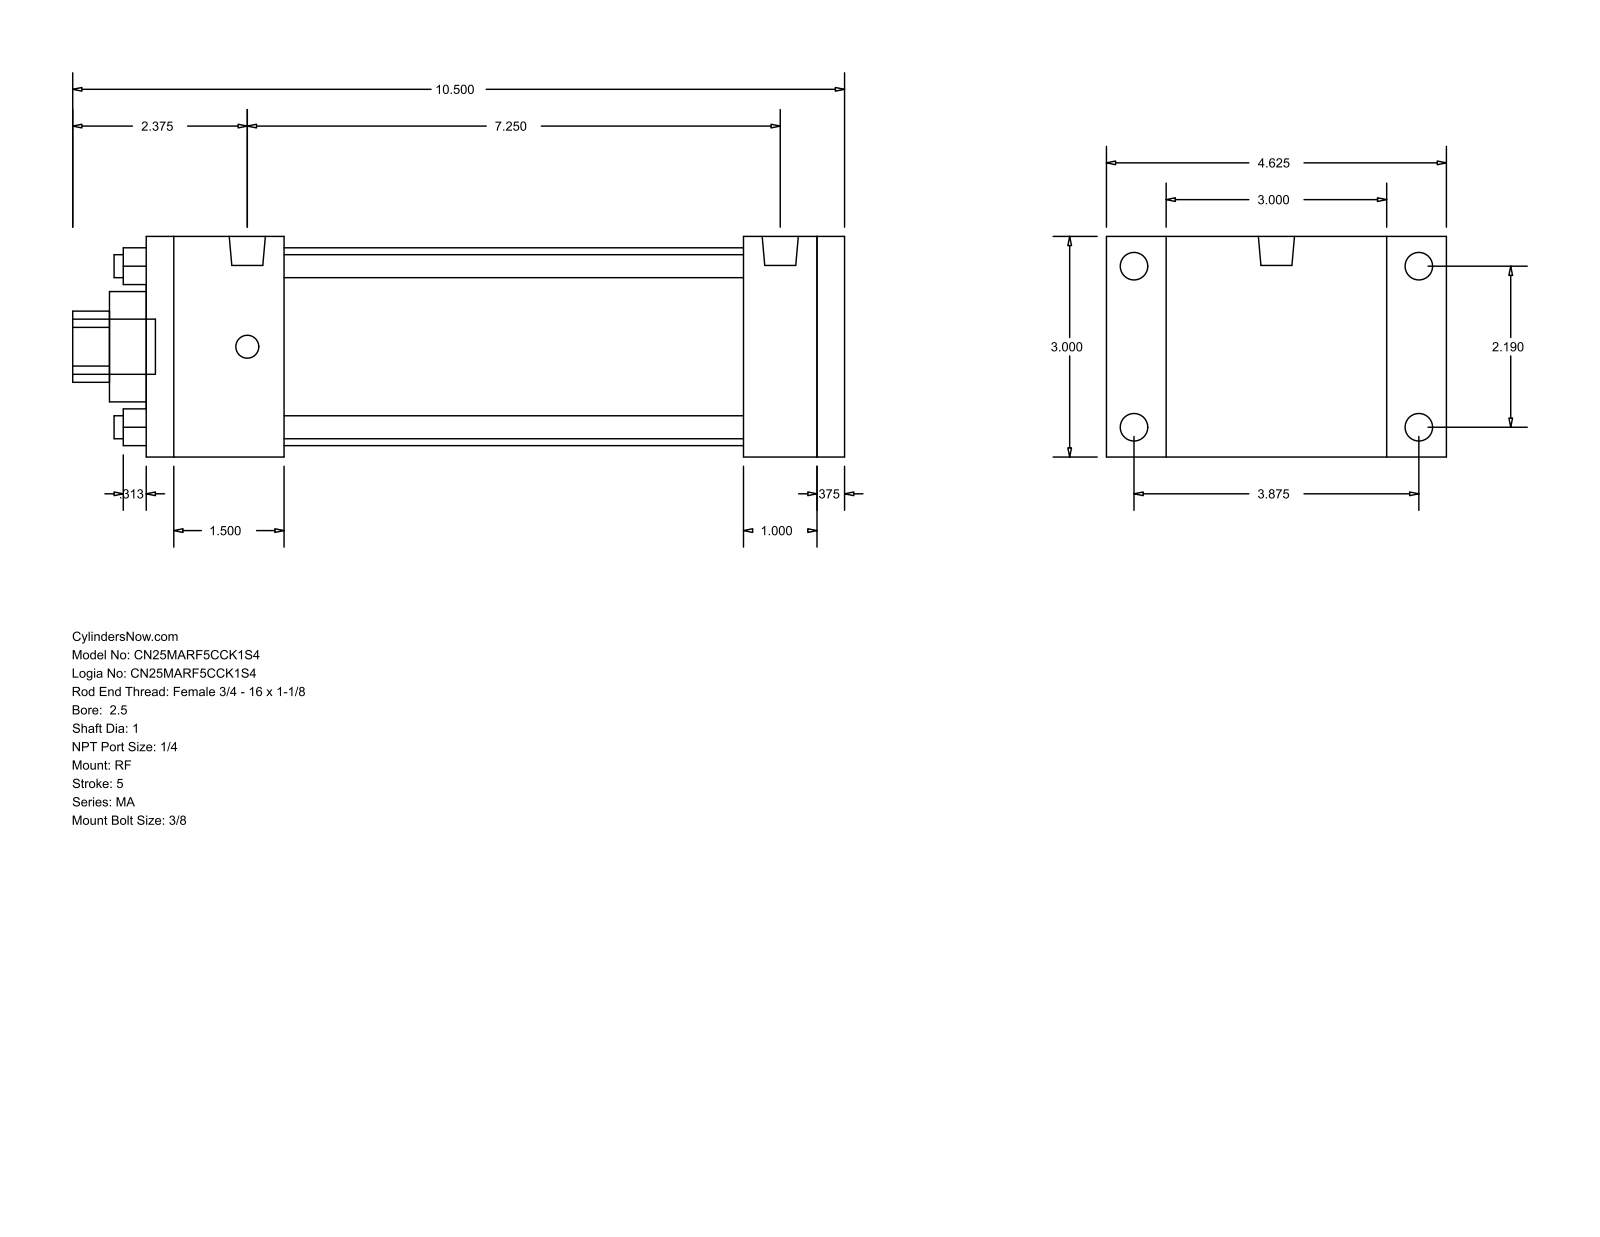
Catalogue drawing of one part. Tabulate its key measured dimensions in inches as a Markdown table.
| quantity | value |
| --- | --- |
| part name | MA_RF__0250_1 |
| STEP written by | GSSL Pune (CONFIG_CONTROL_DESIGN) |
| units | inches |
| bodies | 0 solids, 92 faces (64 planar, 28 cylindrical, 0 other) |
| overall size | 10.5 × 4.625 × 3 |
| round holes (diameter × count) | 0.313 × 4, 1 × 1, 1.5 × 1, 2.69 × 1 |
| round bosses / shafts (diameter × count) | 0.375 × 4, 0.313 × 4, 0.492 × 2, 0.75 × 1 |
| partial cylindrical surfaces (radius × count) | 0.484 × 1 |
| main face-to-face distances | 3, 9.5, 9.125, 0.375, 1, 1.875, 8.125, 6.25, 7.25, 7.625 |
| hole center spacings | 1.548, 2.19, 3.097 |
